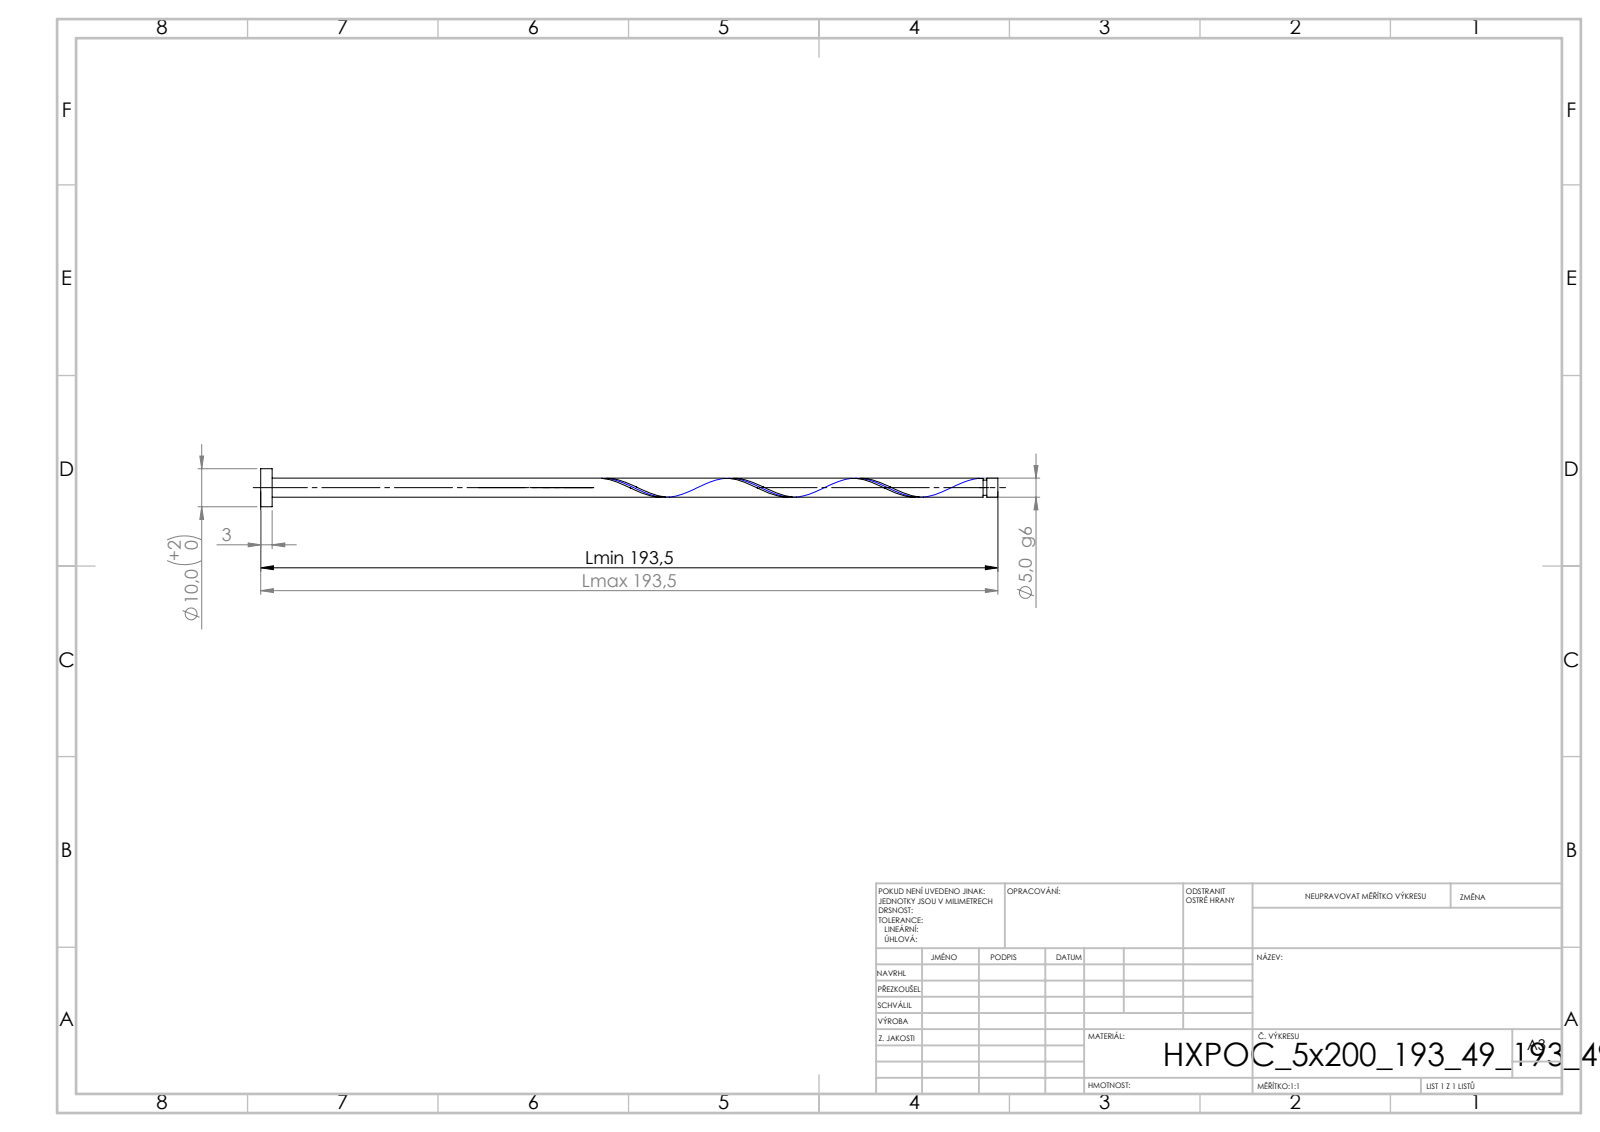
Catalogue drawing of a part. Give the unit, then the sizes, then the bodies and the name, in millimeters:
Units: millimetres
Overall size (bounding box): 193.49 × 10 × 10
Round bosses / shafts (diameter × count): ⌀10 ×1, ⌀5 ×1, ⌀4 ×1
Main face-to-face distances: 3, 193.49, 190.49, 190.6, 187.6, 2.89, 189.6, 186.6, 1, 3.89
Volume: 3 931 mm³ · Surface area: 3 309 mm²
Bodies: 1 solid, 21 faces (6 planar, 14 cylindrical, 1 other)
STEP written by: SolidWorks 2019 (CONFIG_CONTROL_DESIGN)
